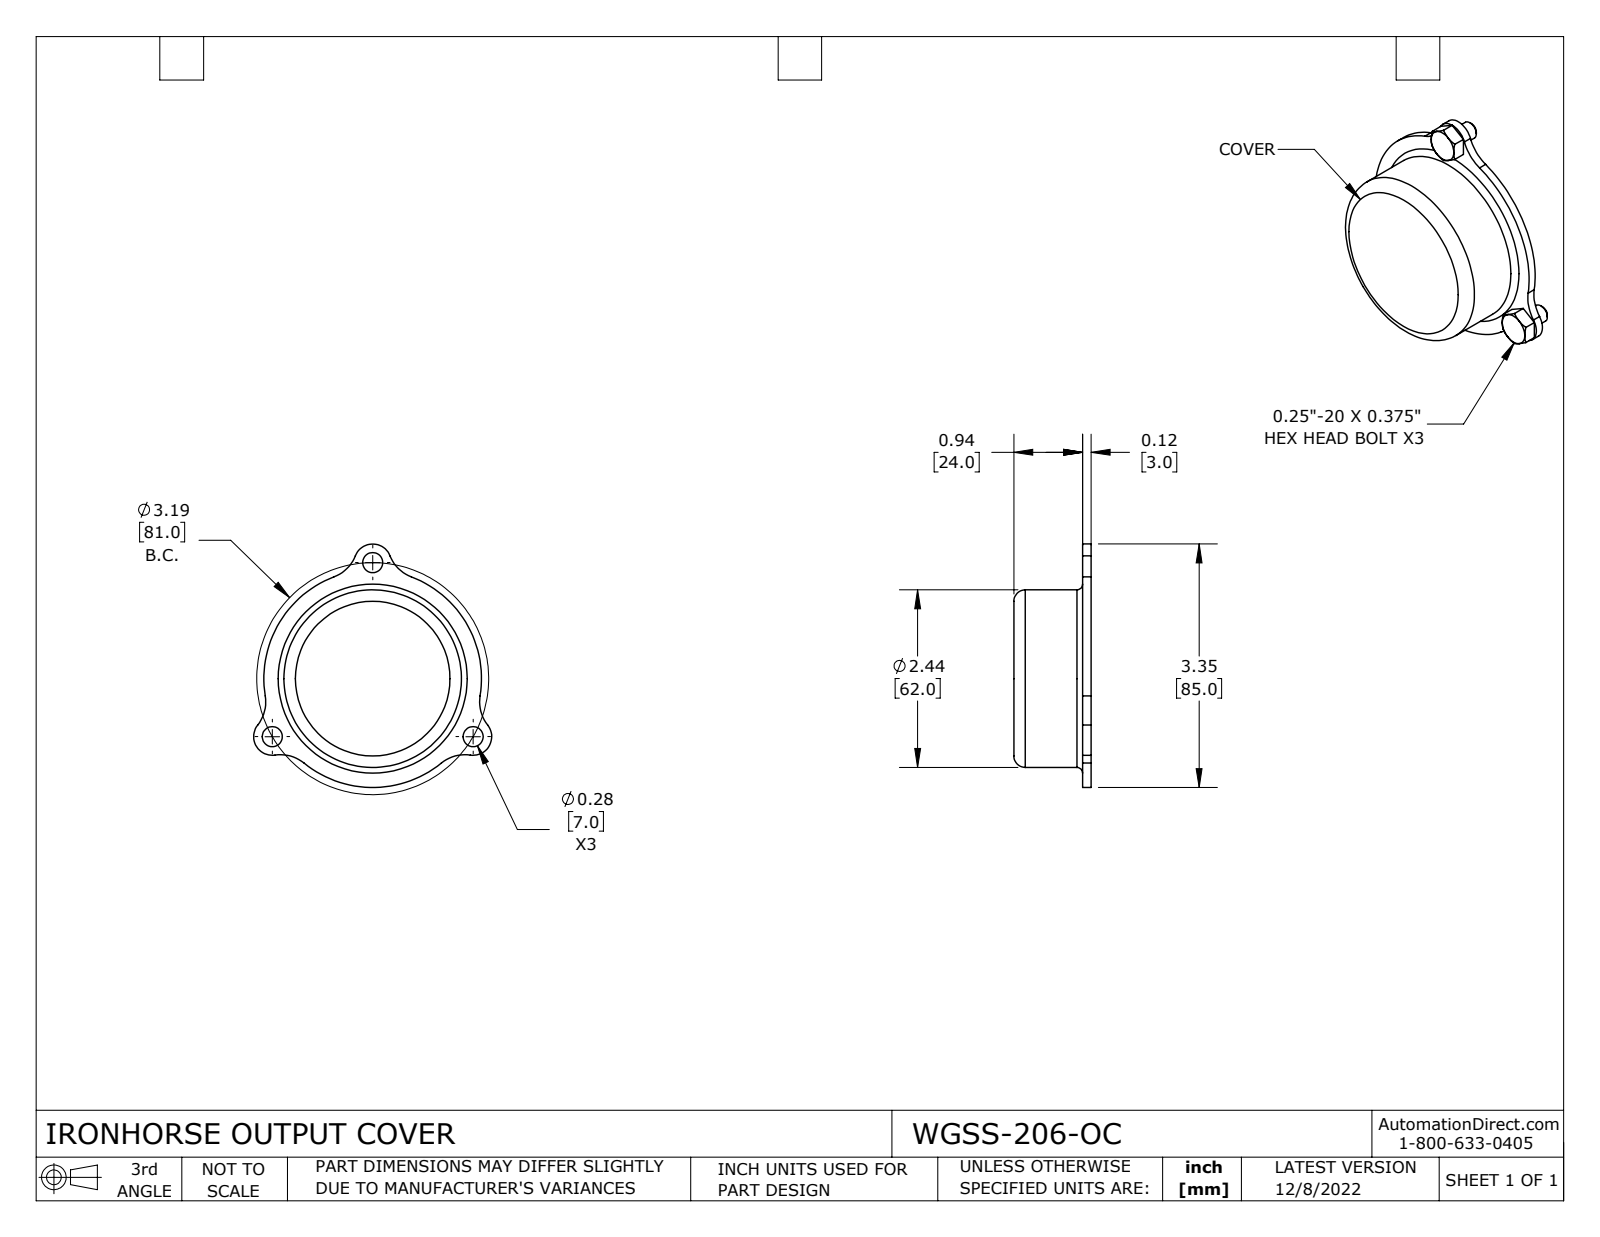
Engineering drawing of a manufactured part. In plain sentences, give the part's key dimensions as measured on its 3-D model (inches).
The part is named "WGSS-206-OC". Its 3-D file was written by "SolidWorks 2021 (CONFIG_CONTROL_DESIGN)". It is 4 solids with 94 faces: 31 planar, 31 cylindrical and 32 other. Overall it measures 3.346 by 3.274 by 1.32 inches. Its volume is 1.354 cubic inches and its surface area 31.84 square inches. Round holes: 3 of diameter 0.276, 1 of diameter 2.283. Round bosses or shafts: 3 of diameter 0.25, 1 of diameter 2.441. Partial cylindrical surfaces (rounded edges, fillets, slot ends): 6 of radius 0.512, 3 of radius 0.256, 1 of radius 1.496. The main face-to-face distances are 0.079, 0.866, 0.945, 0.118, 0.984, 1.063, 0.306, 0.188, 0.678, 0.757. The hole center spacings are 1.594, 2.762, 2.761.
